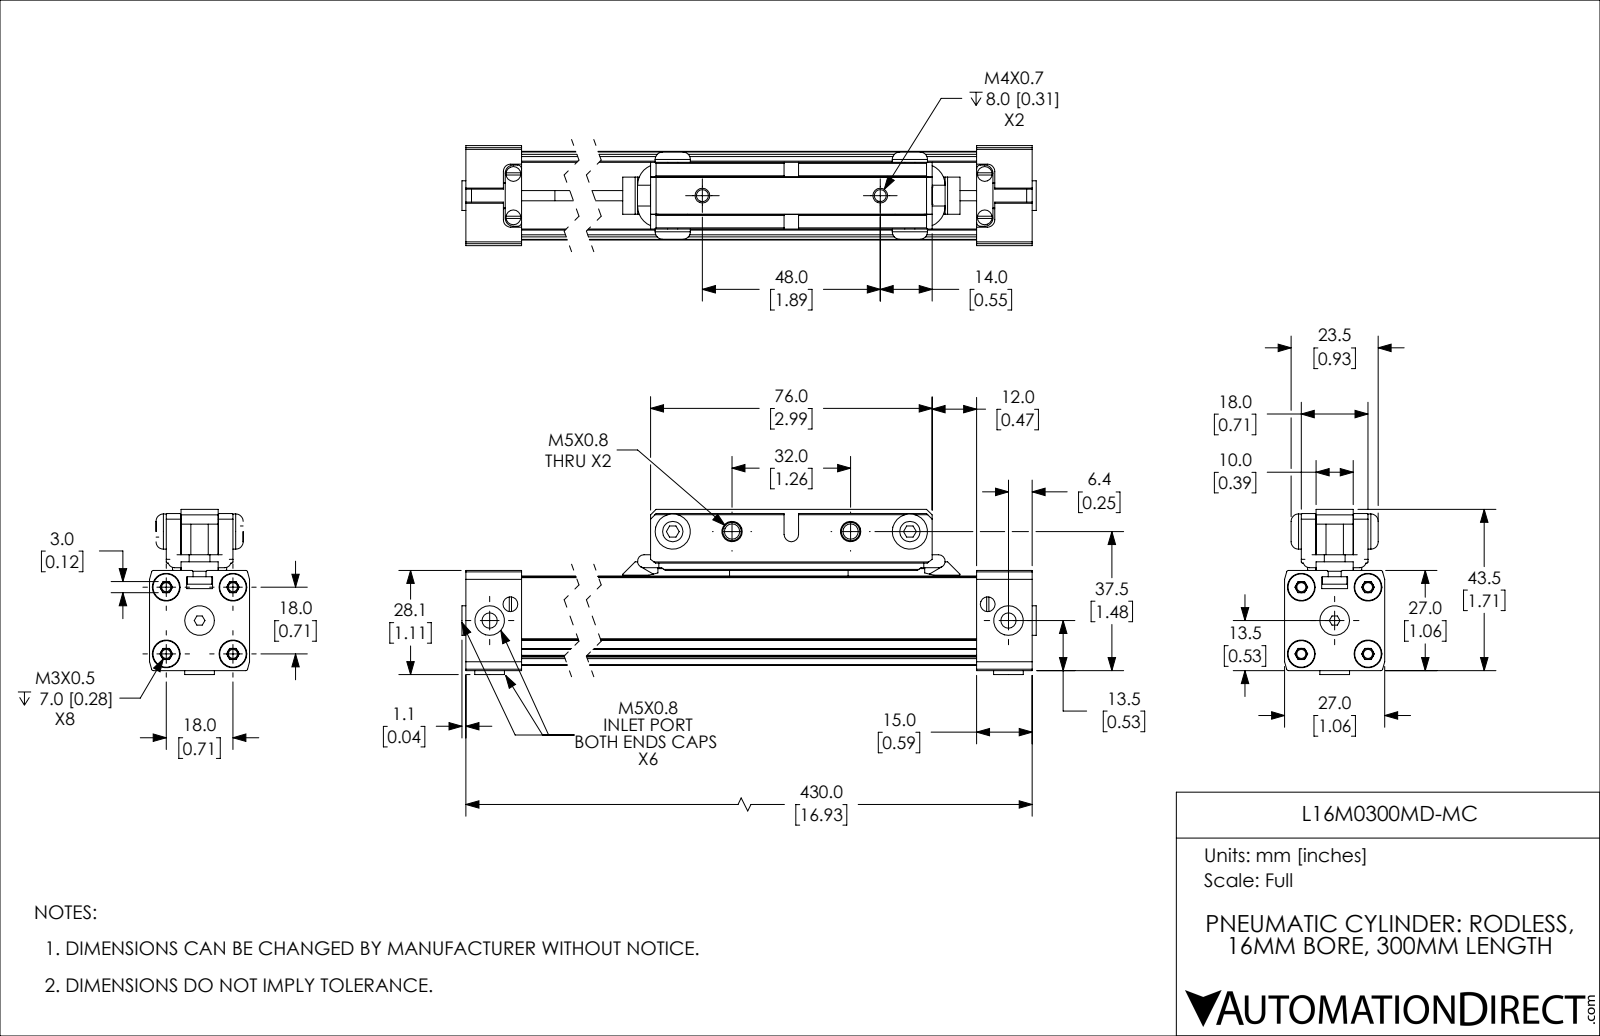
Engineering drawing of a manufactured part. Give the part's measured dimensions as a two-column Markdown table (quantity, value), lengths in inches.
| quantity | value |
| --- | --- |
| part name | L16M0300MD-MC_PISTON; L16M0300MD-MC_BODY; L16M0300MD-MC |
| STEP written by | SolidWorks 2019 (CONFIG_CONTROL_DESIGN) |
| units | inches |
| bodies | 13 solids, 827 faces (435 planar, 284 cylindrical, 108 other) |
| overall size | 17.014 × 1.755 × 1.063 |
| volume | 11.64 in³ |
| surface area | 153.4 in² |
| round holes (diameter × count) | 0.163 × 9, 0.157 × 6, 0.315 × 5, 0.097 × 4, 0.217 × 4, 0.295 × 4, 0.128 × 2, 0.634 × 1 |
| round bosses / shafts (diameter × count) | 0.283 × 4, 0.138 × 4, 0.197 × 3, 0.15 × 3, 0.374 × 2, 0.63 × 1 |
| partial cylindrical surfaces (radius × count) | 0.012 × 22, 0.02 × 14, 0.01 × 8, 0.024 × 6, 0.039 × 6, 0.008 × 4, 0.024 × 4, 0.079 × 4 |
| main face-to-face distances | 0.941, 0.945, 0.417, 0.524, 0.825, 0.116, 0.3, 0.408, 0.059, 1.004 |
| hole center spacings | 0.341, 0.501, 0.709, 16.175, 1.89, 0.28, 0.461, 0.469 |
